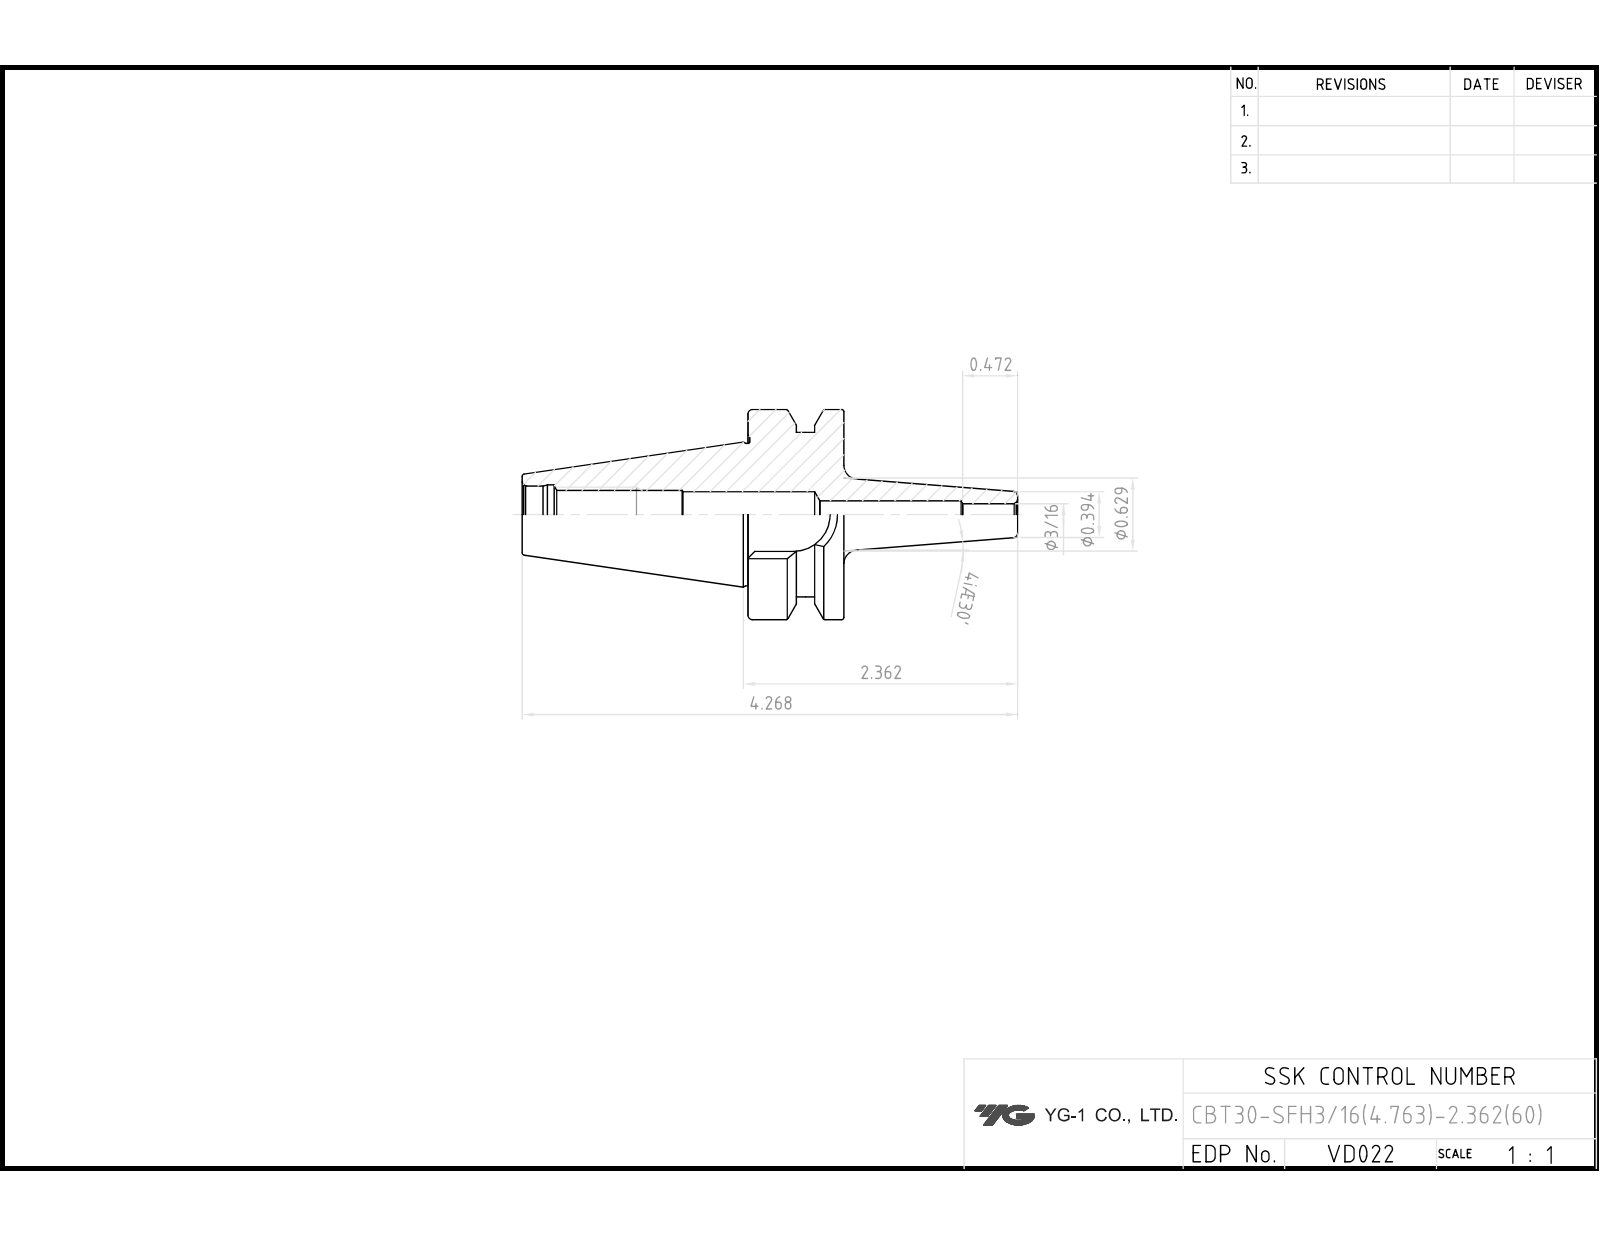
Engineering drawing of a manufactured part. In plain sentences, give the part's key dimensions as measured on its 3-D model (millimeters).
The part is named "CBT30-SFH4_7625-60". Its 3-D file was written by "CREO PARAMETRIC BY PTC INC, 2018500 (CONFIG_CONTROL_DESIGN)". It is 1 solid with 100 faces: 26 planar, 28 cylindrical and 46 other. Overall it measures 108.4 by 46 by 46 millimeters. Its volume is 51 927 cubic millimeters and its surface area 15 225 square millimeters. Round holes: 1 of diameter 4.76, 1 of diameter 6, 1 of diameter 10, 1 of diameter 10.2, 1 of diameter 12, 1 of diameter 12.5, 1 of diameter 13.1. Round bosses or shafts: 1 of diameter 46, 1 of diameter 31.2. Partial cylindrical surfaces (rounded edges, fillets, slot ends): 1 of radius 8.05, 1 of radius 18. The main face-to-face distances are 21, 32.6, 14.63, 6.37, 10.63, 4, 10.37, 0.4, 10.23, 14.23.
